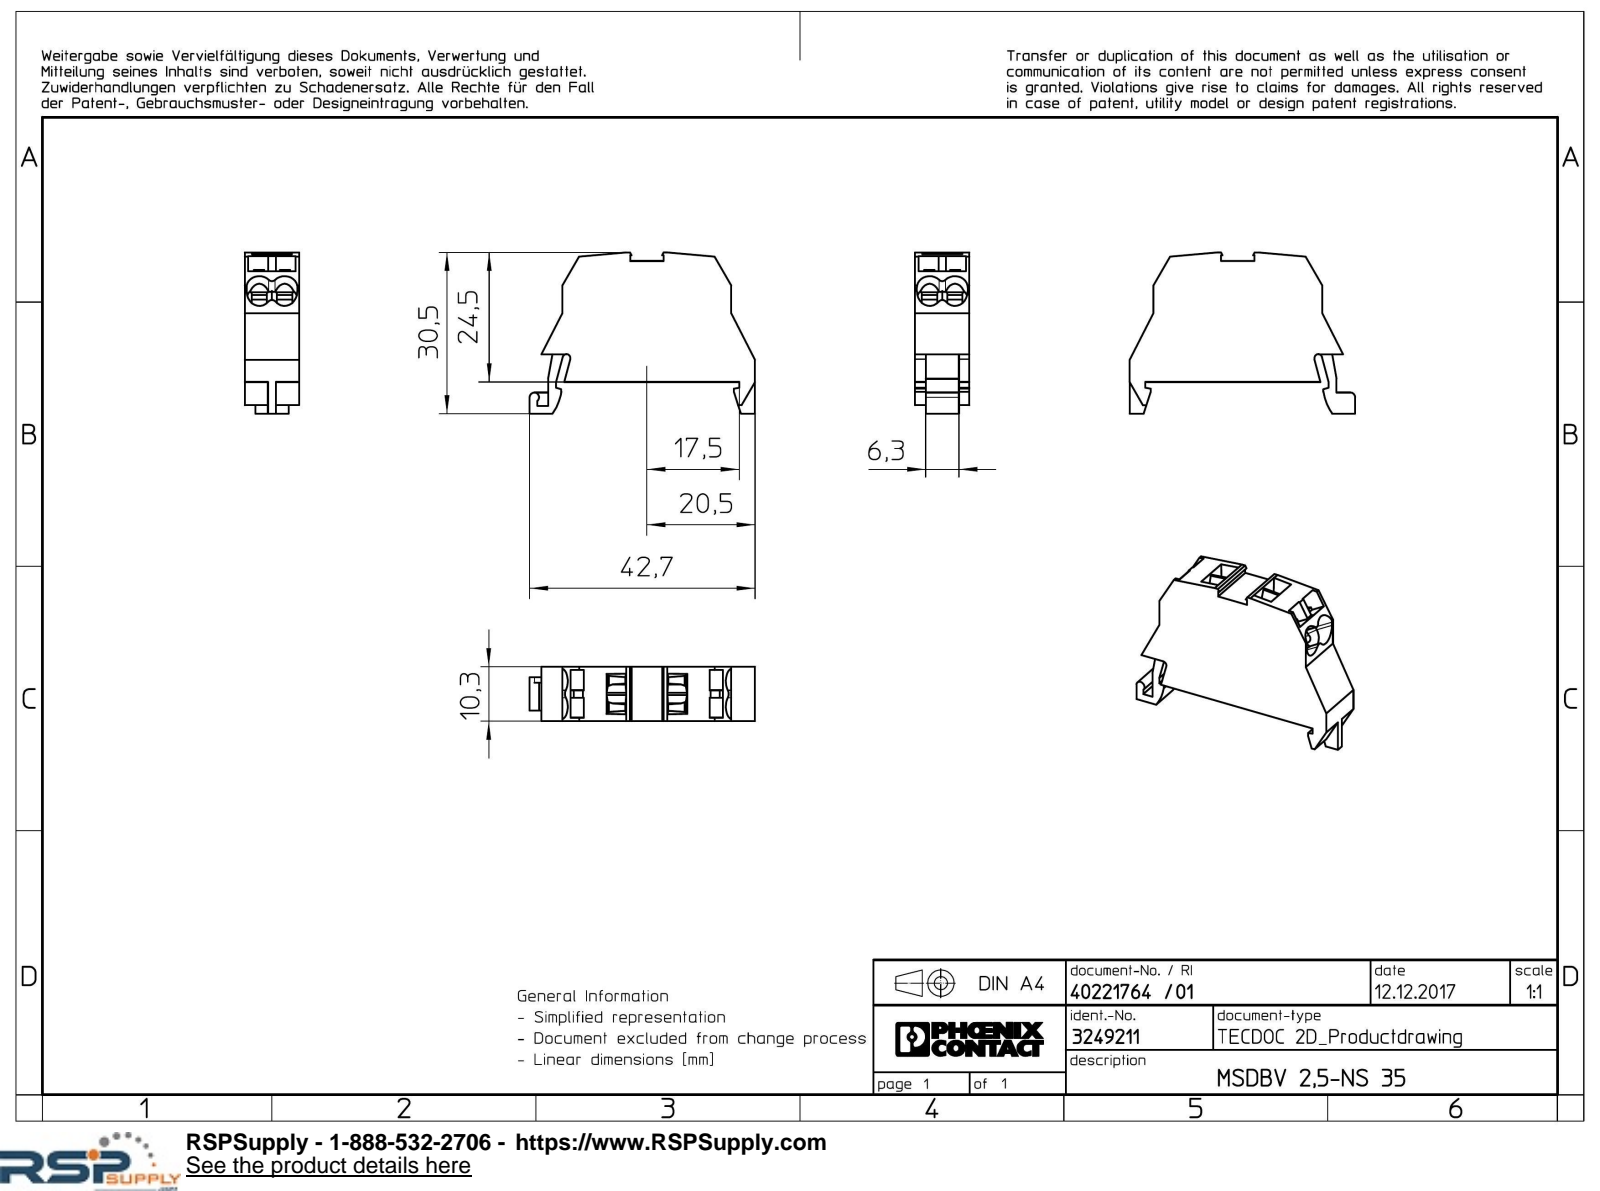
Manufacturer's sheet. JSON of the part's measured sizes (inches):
{"part_name": "MSDBV_2.5-NS_35-select", "step_written_by": "Creo Elements/Direct Modeling 18.1I 14-Aug-2016 (C) Parametric Technology GmbH (AUTOMOTIVE_DESIGN)", "units": "inches", "bodies": {"solids": 1, "faces": 209, "planar": 174, "cylindrical": 23, "other": 12}, "overall_size": [1.681, 1.201, 0.406], "volume_in3": 0.437, "surface_area_in2": 7.164, "partial_cylinders_radius": [[0.039, 10], [0.094, 8], [0.031, 2], [0.03, 1], [0.035, 1], [0.374, 1]], "face_to_face_distances": [0.406, 0.026, 0.38, 0.354, 0.175, 0.23, 0.15, 0.205, 0.066, 0.185]}
